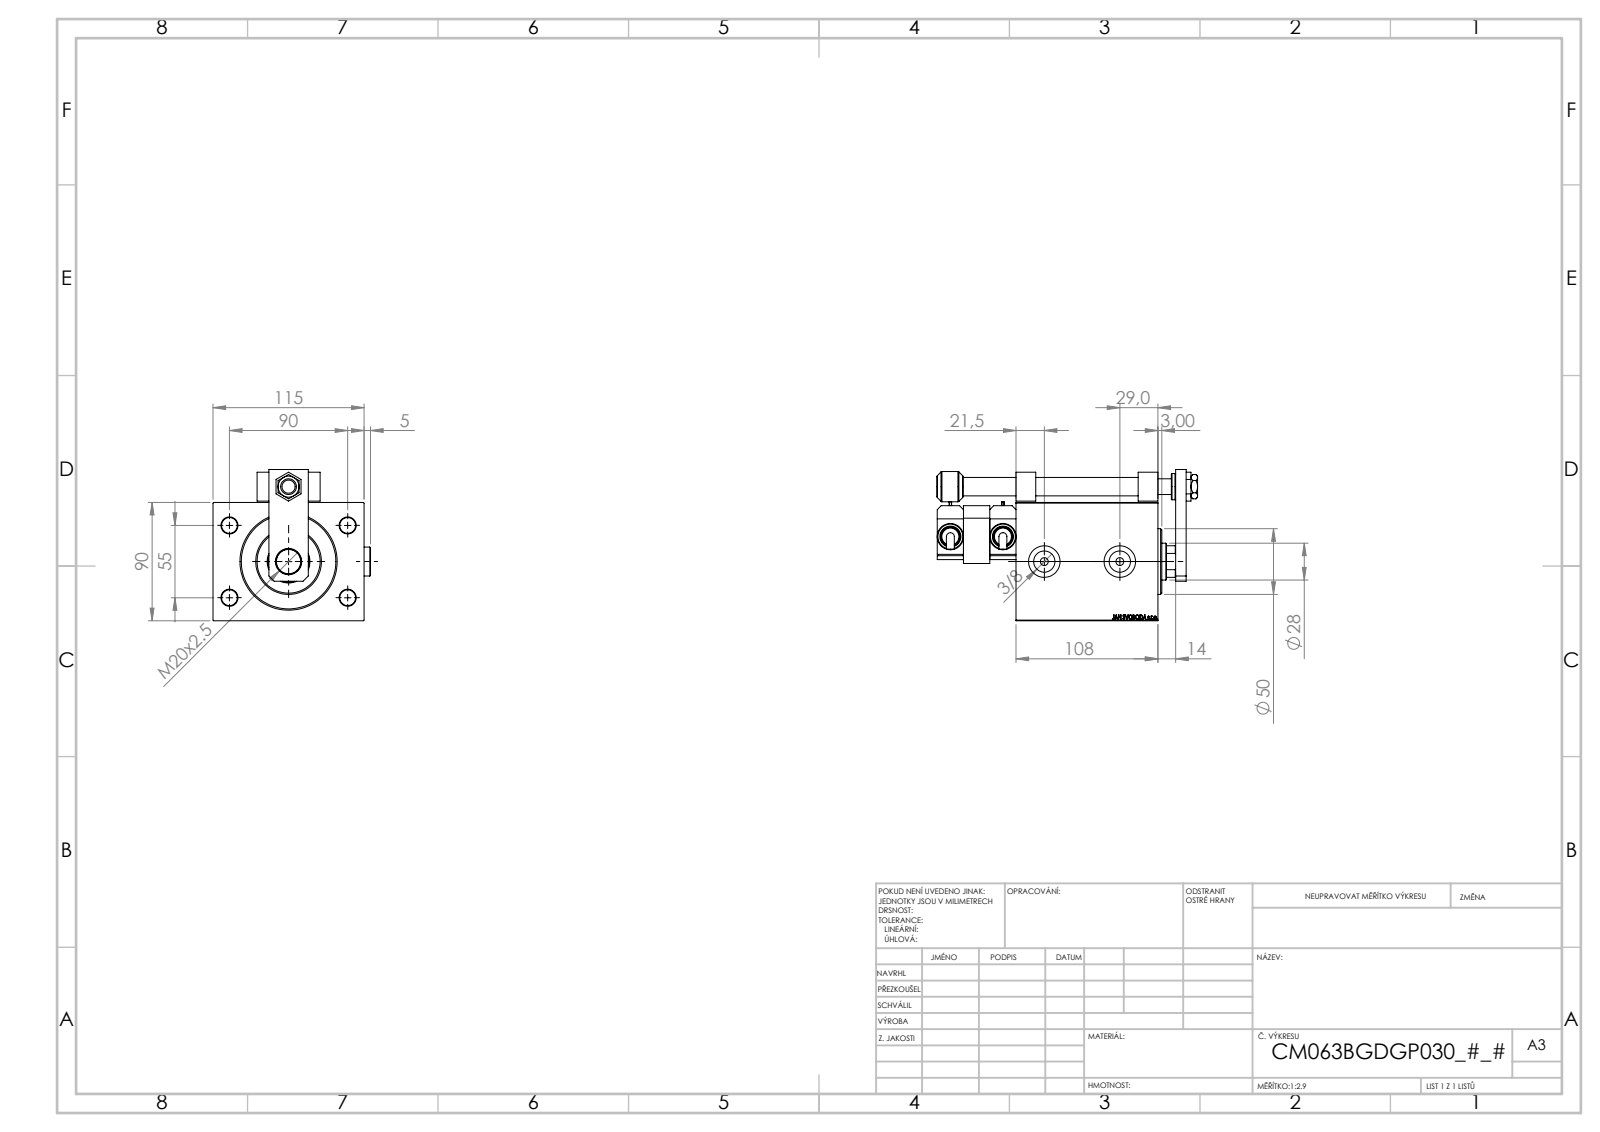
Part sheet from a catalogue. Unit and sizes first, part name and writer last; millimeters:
Units: millimetres
Overall size (bounding box): 198.5 × 119.9 × 115
Round holes (diameter × count): ⌀12 ×5, ⌀4 ×4, ⌀8 ×4, ⌀6 ×2, ⌀16.17 ×2, ⌀24 ×2, ⌀13 ×1, ⌀14 ×1, ⌀18.5 ×1, ⌀20 ×1, ⌀28 ×1, ⌀31.5 ×1
Round bosses / shafts (diameter × count): ⌀20 ×3, ⌀22 ×2, ⌀16 ×2, ⌀14 ×2, ⌀6 ×2, ⌀50 ×1, ⌀23 ×1
Partial cylindrical surfaces — rounded edges, fillets, slot ends (radius × count): R3 ×1, R13.5 ×1
Main face-to-face distances: 90, 115, 108, 20, 17.5, 37.5, 90.5, 40, 13.5, 43.5
Hole centre spacings: 52.74, 20, 53.81, 55, 90, 93, 95.13, 95.74
Volume: 1 194 000 mm³ · Surface area: 179 007 mm²
Bodies: 16 solids, 1163 faces (548 planar, 130 cylindrical, 485 other)
Part name (STEP PRODUCT): TYC_P; KROUZEK_PRO_TYC; V450CM_B_Body; ZARAZKA_P (+8 more)
STEP written by: SolidWorks 2019 (CONFIG_CONTROL_DESIGN)
